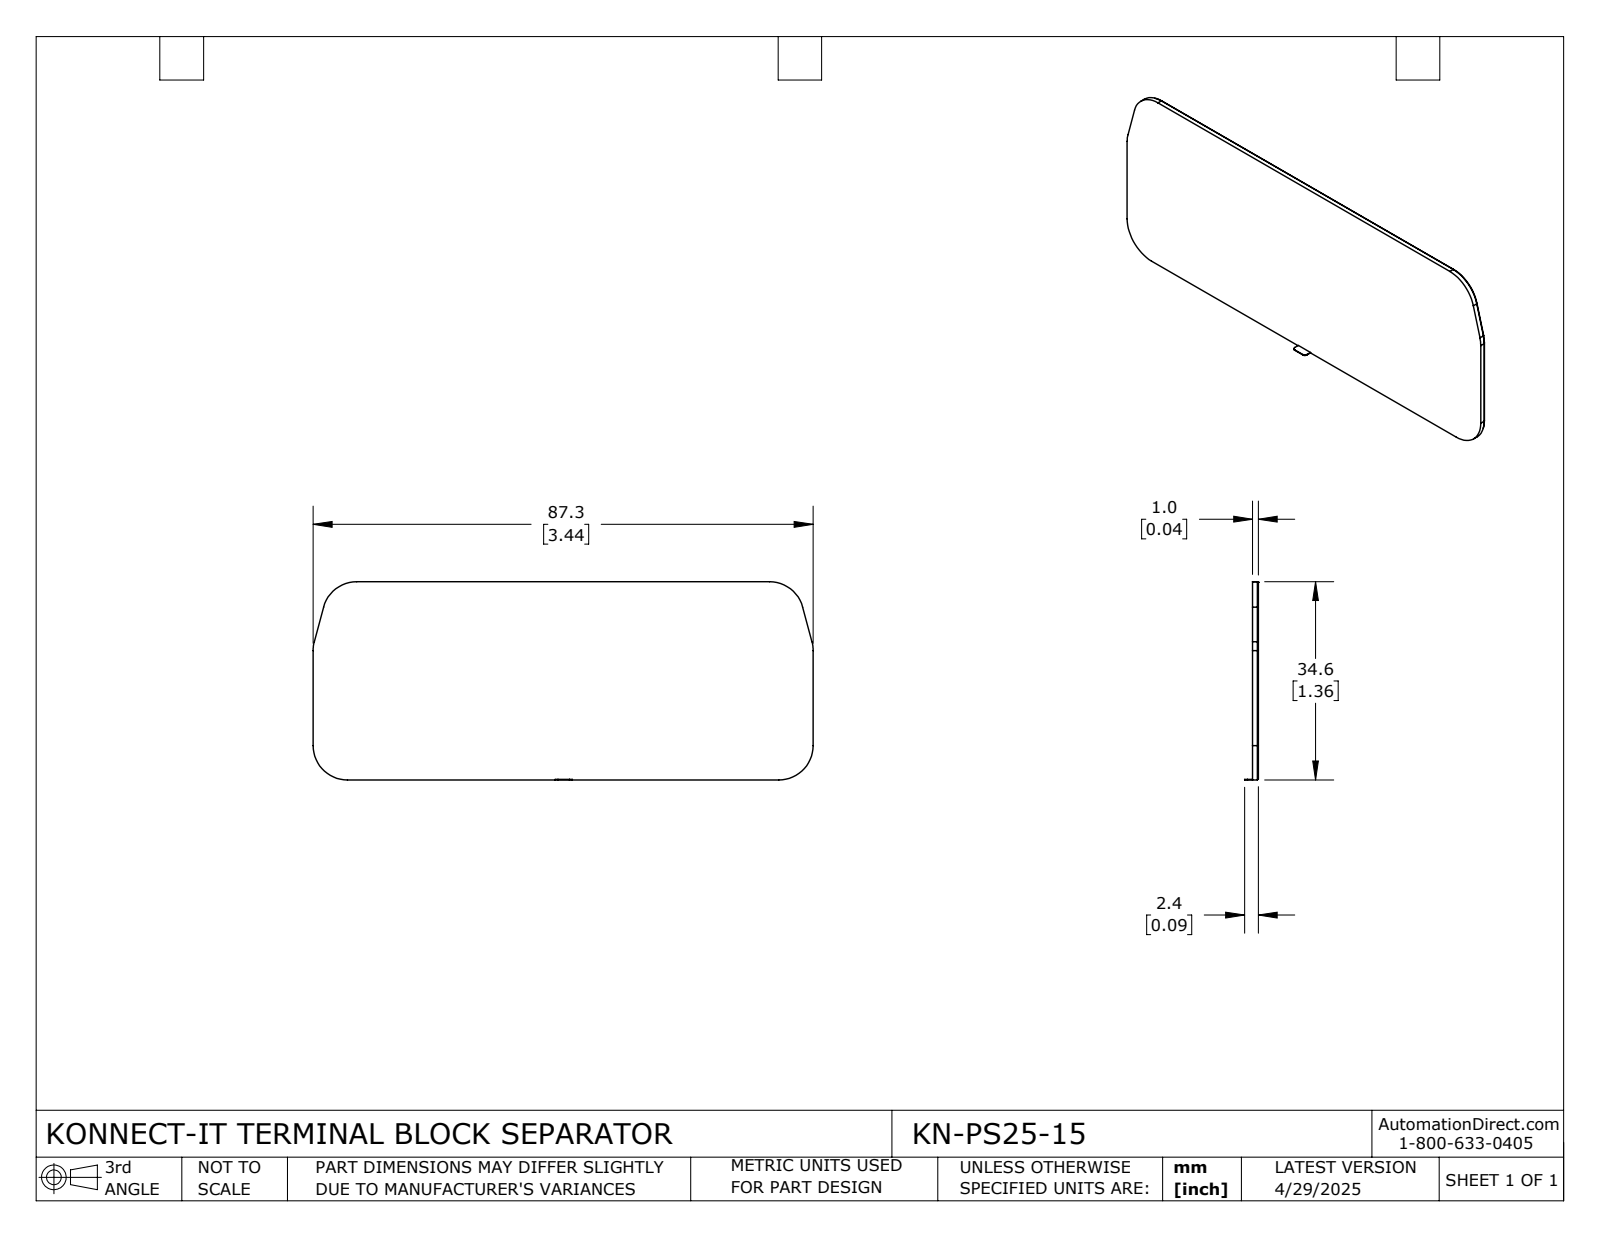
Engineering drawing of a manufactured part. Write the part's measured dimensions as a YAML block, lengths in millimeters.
part_name: "KN-PS25-15"
step_written_by: "SolidWorks 2024 (CONFIG_CONTROL_DESIGN)"
units: millimeters
bodies: {solids: 1, faces: 33, planar: 19, cylindrical: 14, other: 0}
overall_size: [87.31, 34.61, 2.4]
volume: 2961
surface_area: 6168
partial_cylinders:
  - {radius: 5.9, count: 6}
  - {radius: 6, count: 6}
  - {radius: 0.5, count: 2}
face_to_face_distances: [1, 34.61, 34.51, 0.85, 87.31, 34.41, 87.21, 87.11, 1.4, 2.25]
